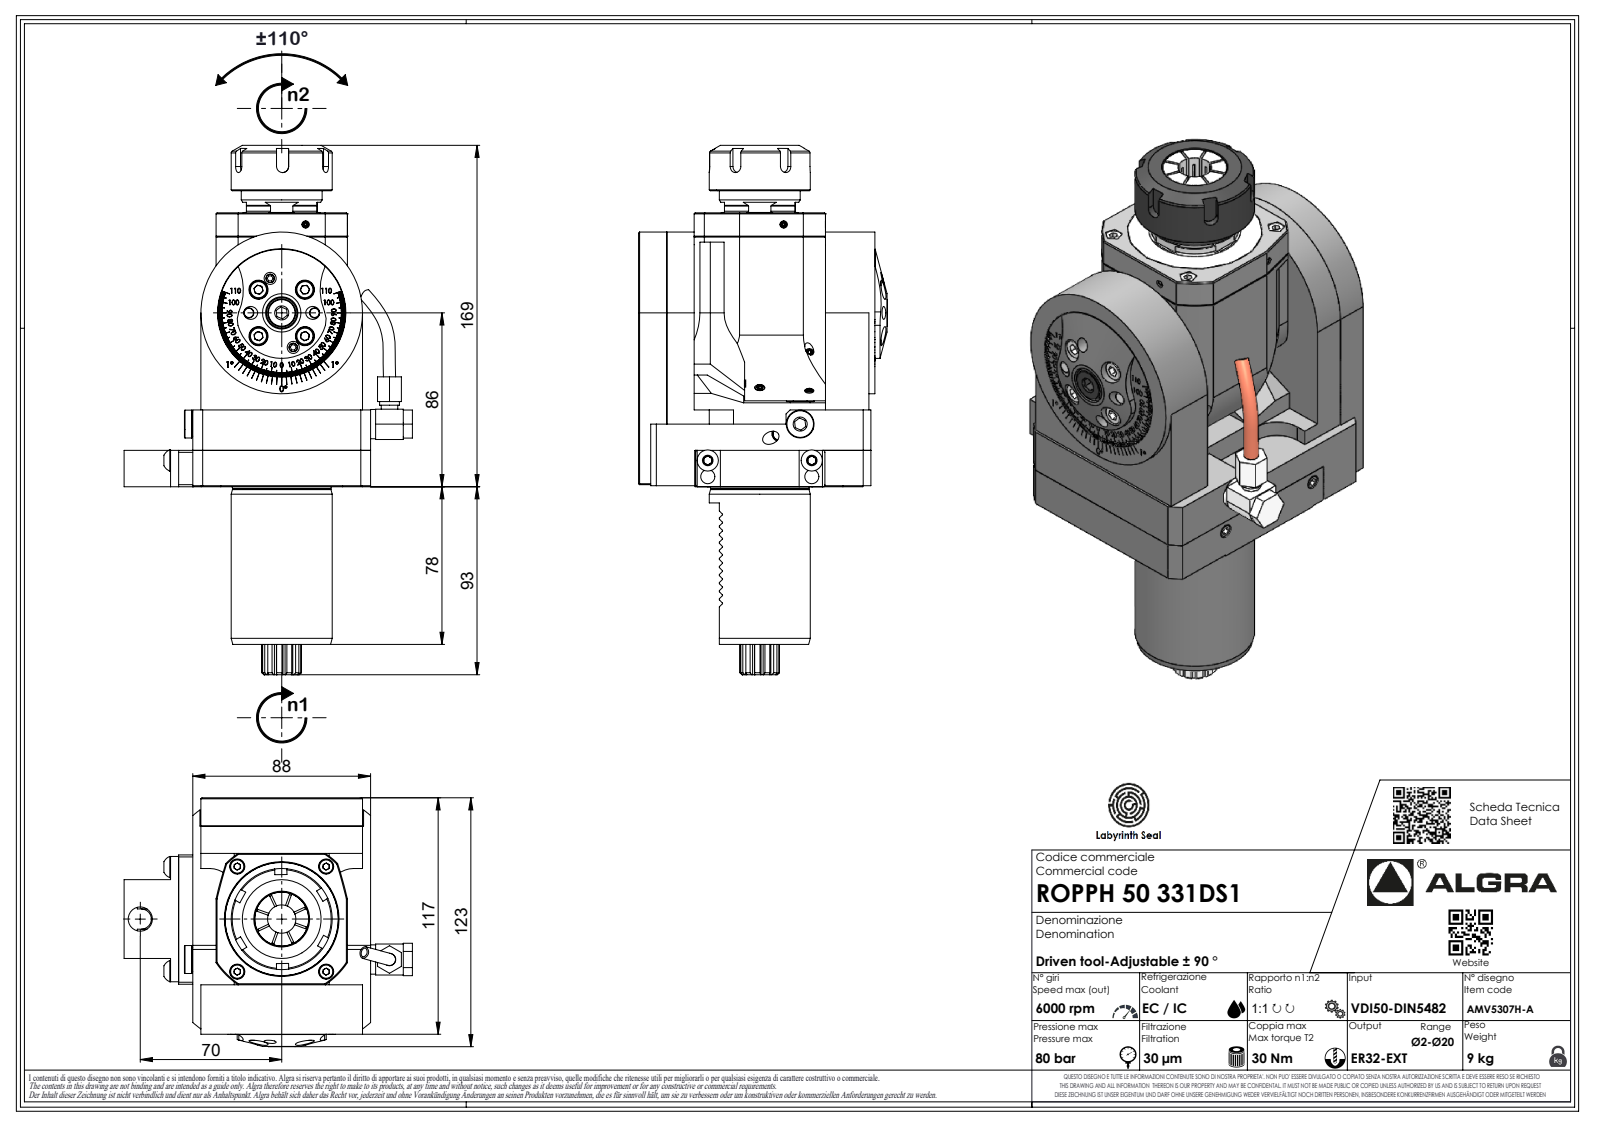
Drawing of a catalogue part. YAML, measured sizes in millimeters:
part_name: "ROPPH50331DS1"
step_written_by: "SolidWorks 2023 (AUTOMOTIVE_DESIGN)"
units: millimeters
bodies: {solids: 1, faces: 674, planar: 387, cylindrical: 142, other: 145}
overall_size: [261.91, 142.7, 123]
volume: 1280000
surface_area: 112037
round_holes:
  - {diameter: 2.1, count: 1}
round_bosses_or_shafts:
  - {diameter: 80, count: 1}
  - {diameter: 50, count: 1}
  - {diameter: 48.7, count: 1}
  - {diameter: 40, count: 1}
  - {diameter: 14.5, count: 1}
  - {diameter: 9.8, count: 1}
  - {diameter: 8.2, count: 1}
  - {diameter: 6.37, count: 1}
partial_cylinders:
  - {radius: 9.38, count: 24}
  - {radius: 0.3, count: 12}
  - {radius: 0.33, count: 7}
  - {radius: 0.52, count: 7}
  - {radius: 3.7, count: 7}
  - {radius: 3, count: 5}
  - {radius: 1, count: 4}
  - {radius: 10, count: 2}
face_to_face_distances: [4, 65, 84, 0.5, 76.5, 11.5, 22.5, 27.5, 7.5, 72.5]
